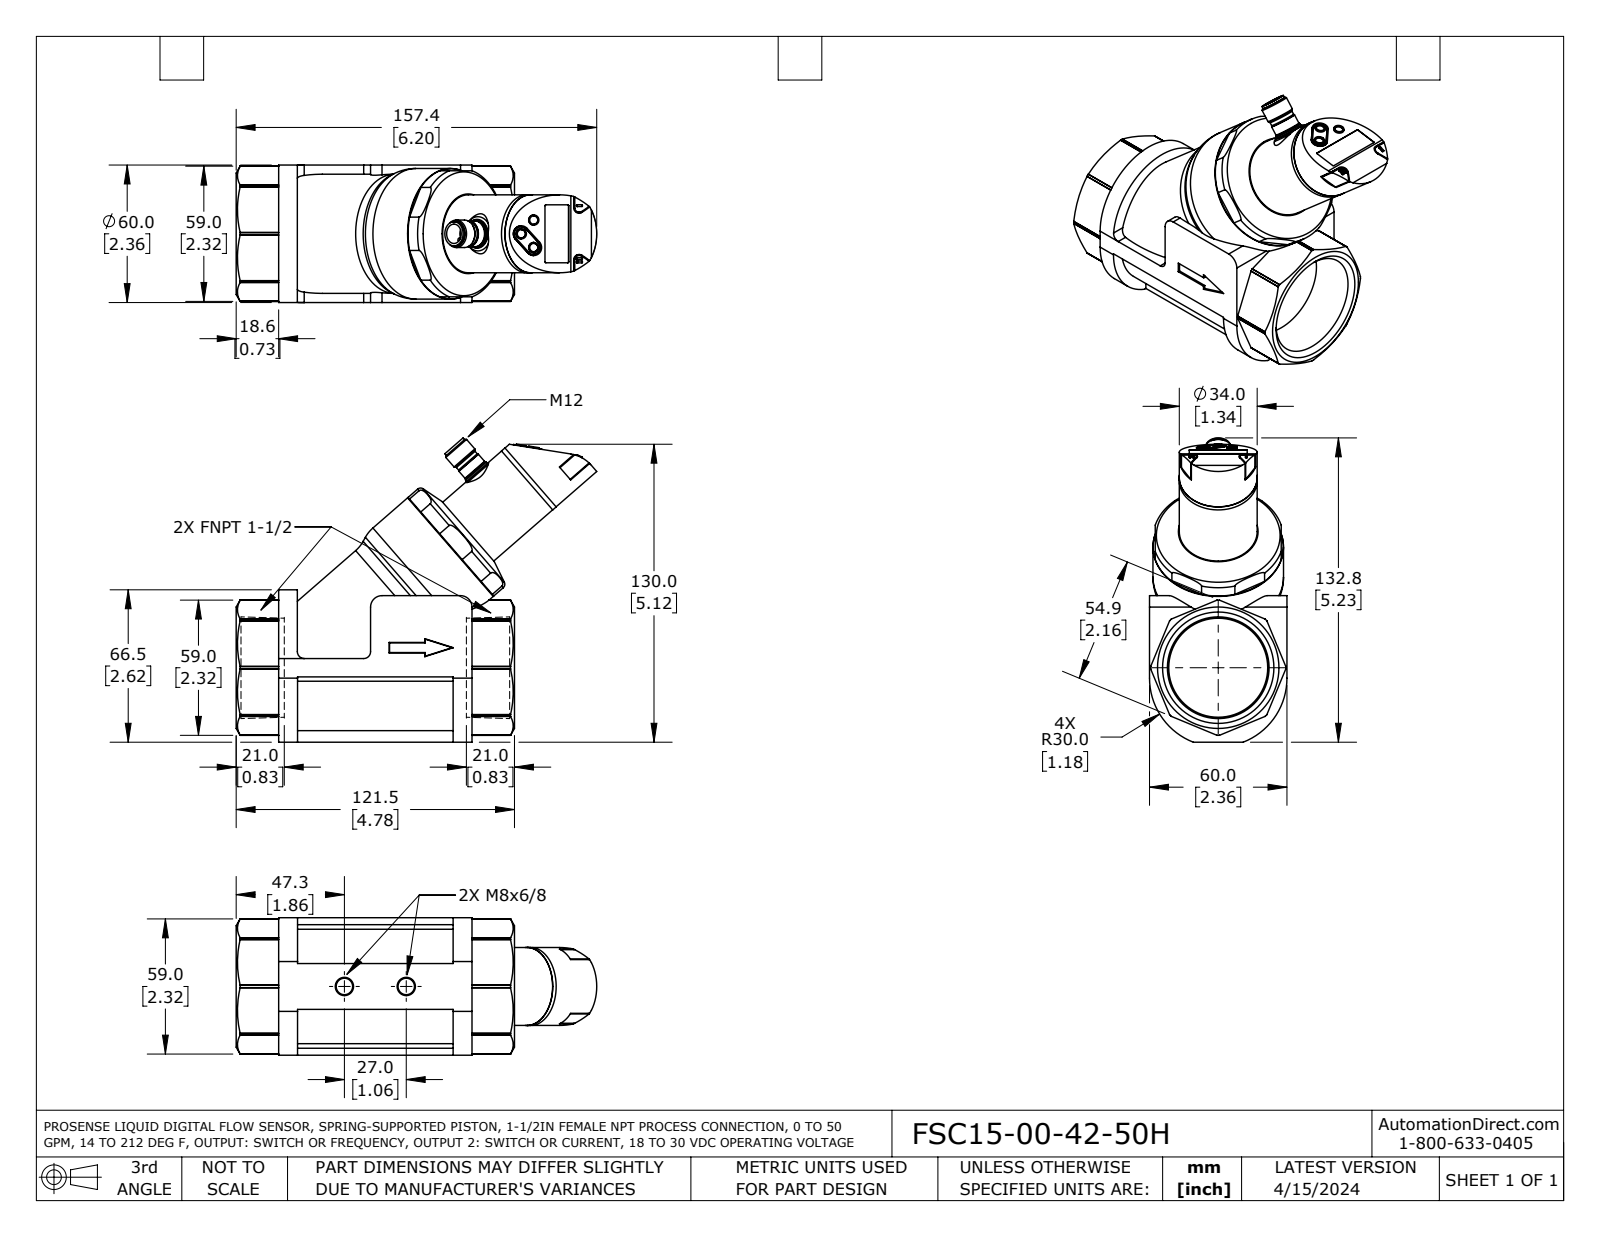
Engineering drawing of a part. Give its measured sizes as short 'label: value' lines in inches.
name: FSC15-00-42-50H
written by: SolidWorks 2021 (AUTOMOTIVE_DESIGN)
unit: in
bodies: 2 solids, 319 faces (122 planar, 149 cylindrical, 48 other)
size: 6.197 × 5.227 × 2.362
volume: 19.4 in³; area: 96.45 in²
holes: 3× ⌀0.144, 2× ⌀0.283, 1× ⌀0.333, 1× ⌀1.732
bosses: 3× ⌀0.175, 2× ⌀1.339, 1× ⌀2.244, 1× ⌀1.343, 1× ⌀0.472, 1× ⌀0.445, 1× ⌀0.425, 1× ⌀0.415
rounds: 12× R0.008, 8× R0.059, 4× R0.016, 4× R0.118, 2× R0.071, 2× R0.079, 2× R0.087, 2× R0.138
face distances: 2.362, 2.162, 2.161, 0.787, 3.323, 0.73, 4.053, 1.575, 1.055, 3.729
hole spacings: 0.32, 0.472, 1.063
